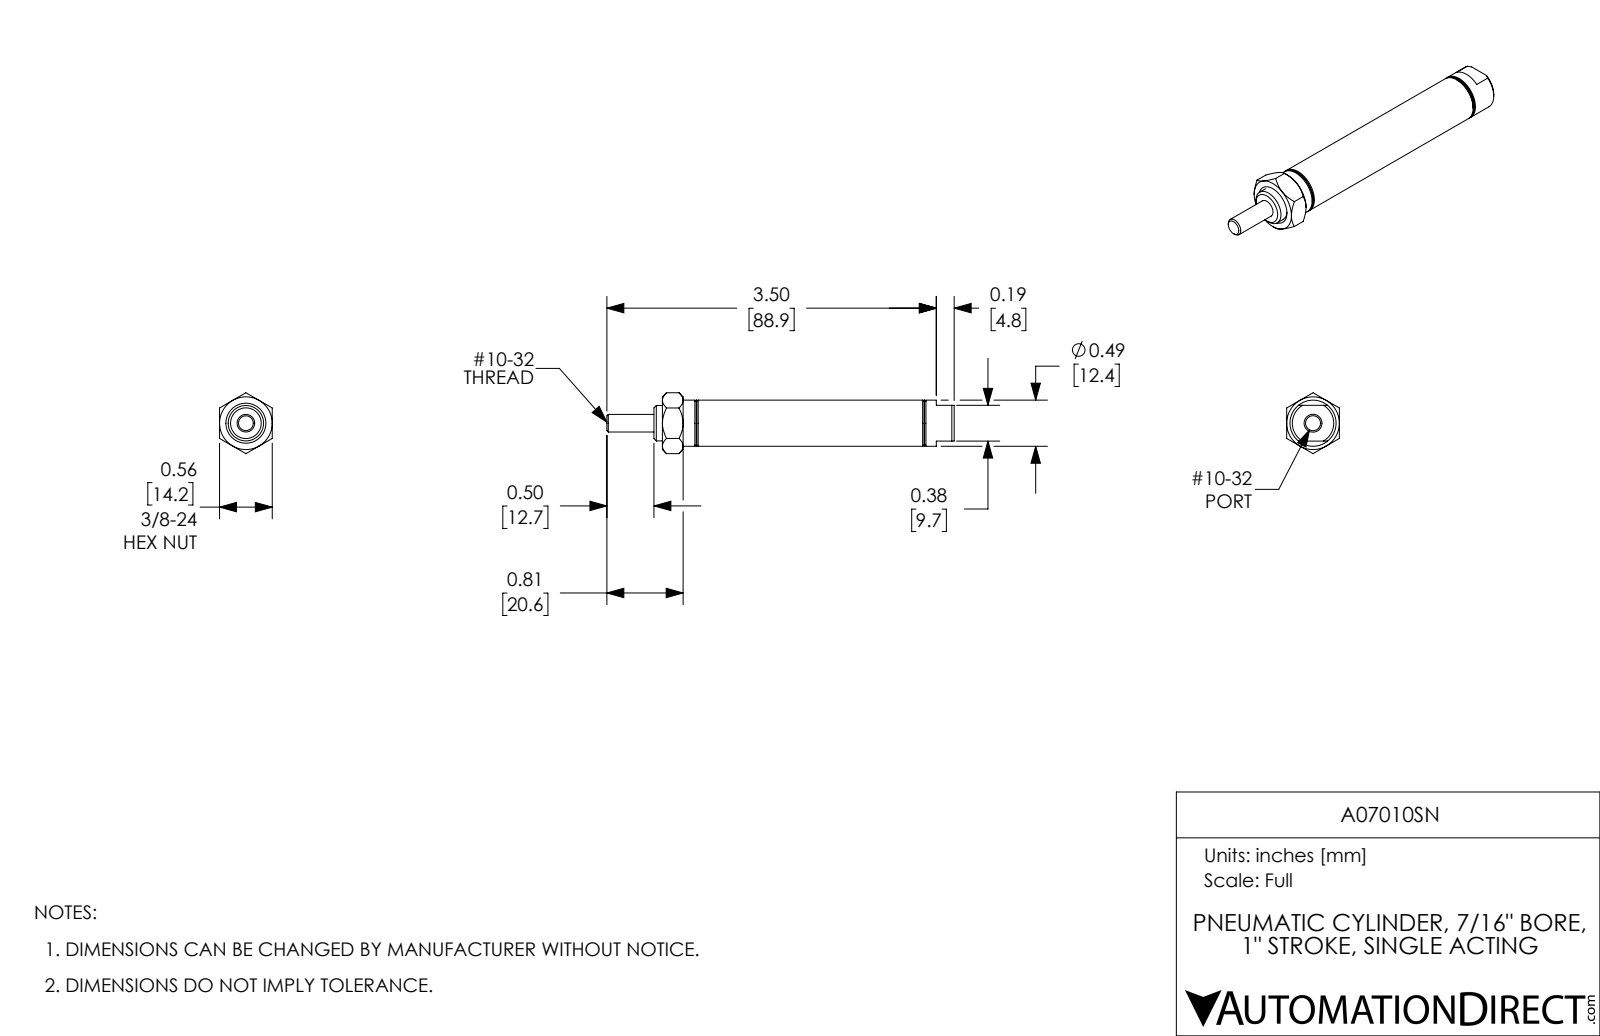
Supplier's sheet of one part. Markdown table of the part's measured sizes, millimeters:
| quantity | value |
| --- | --- |
| part name | A07010SN-Rod; A07010SN_Mounting Nut_D-801; A07010SN-MainBody; A07010SN |
| STEP written by | SolidWorks 2017 (AUTOMOTIVE_DESIGN) |
| units | millimeters |
| bodies | 3 solids, 84 faces (25 planar, 26 cylindrical, 33 other) |
| overall size | 93.7 × 16.4 × 14.2 |
| volume | 7 900 mm³ |
| surface area | 7 645 mm² |
| round holes (diameter × count) | 4 × 1, 4.7 × 1, 4.8 × 1, 9.5 × 1, 11.1 × 1 |
| round bosses / shafts (diameter × count) | 12.4 × 1, 9.6 × 1 |
| main face-to-face distances | 55.6, 17.5, 25.4, 14.2, 12.7, 38.1, 42.9, 30.2, 73.2, 78.7 |
